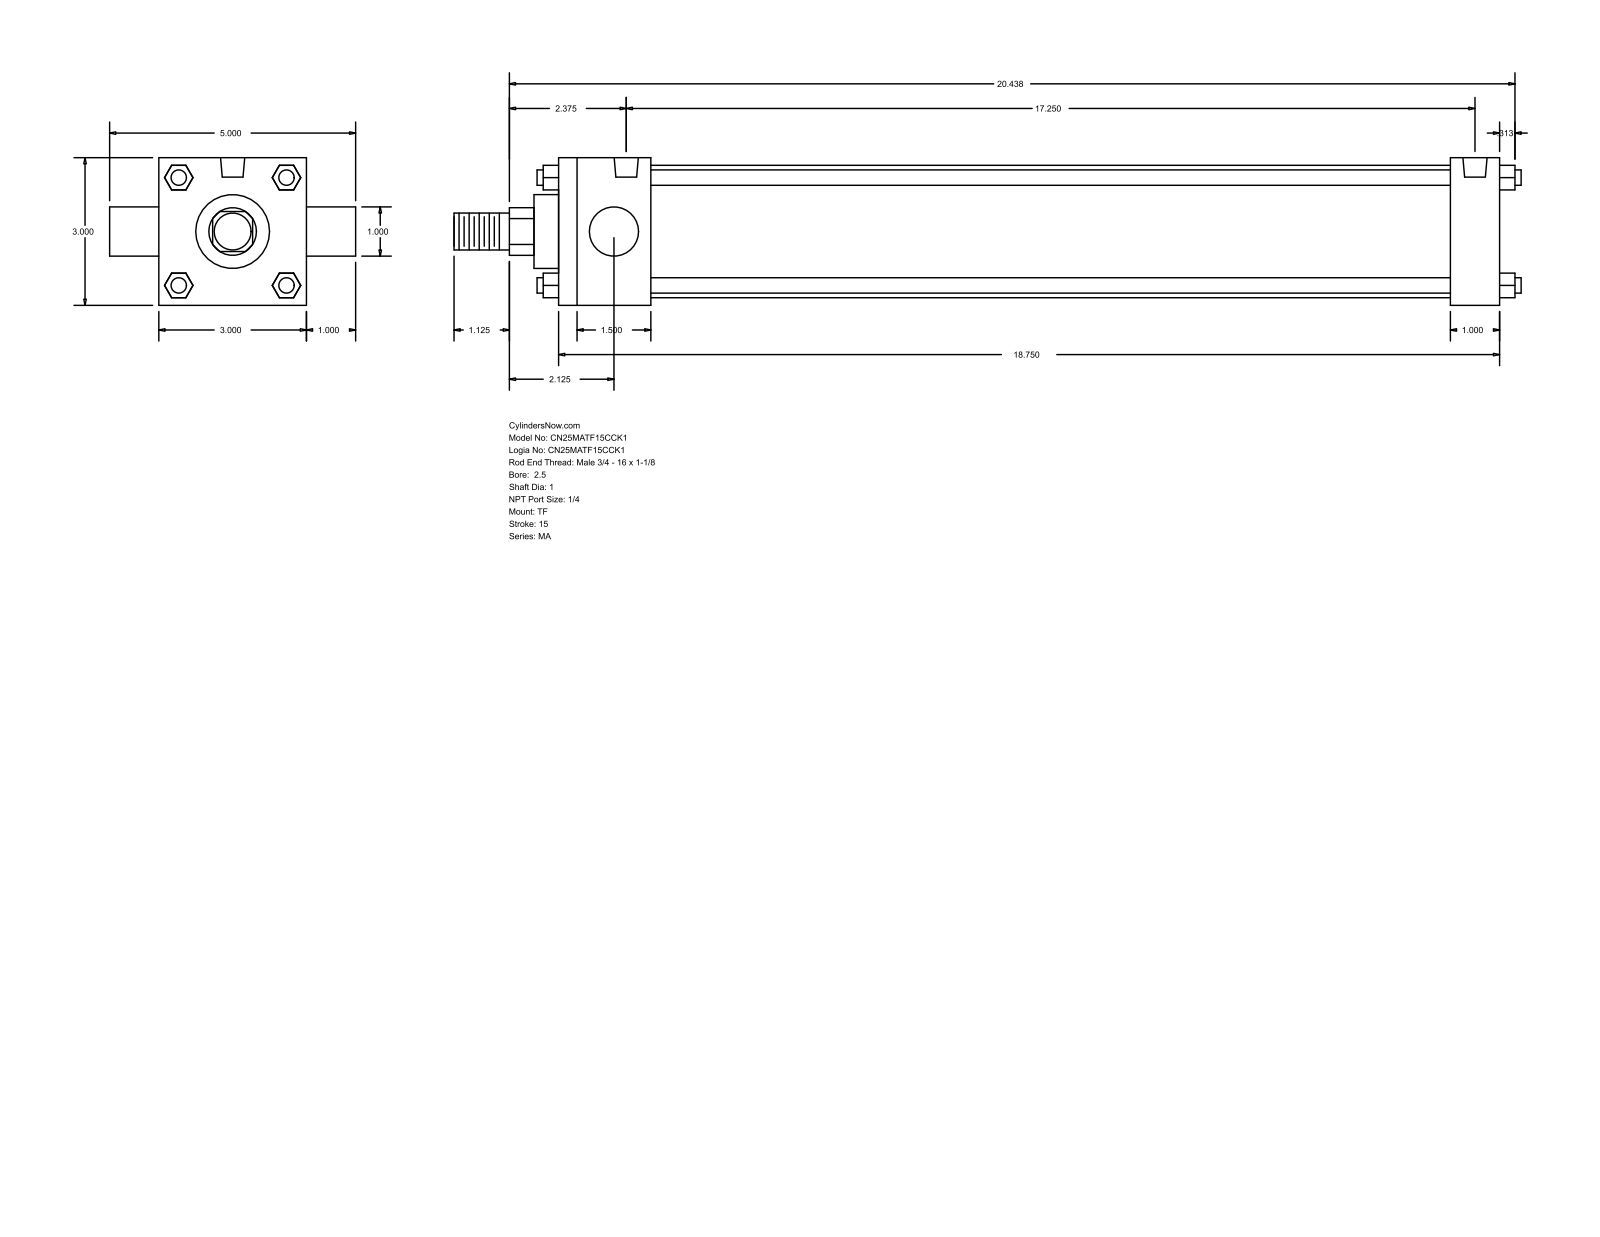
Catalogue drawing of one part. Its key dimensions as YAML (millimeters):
part_name: "MA_TF__0250_1"
step_written_by: "GSSL Pune (CONFIG_CONTROL_DESIGN)"
units: millimeters
bodies: {solids: 0, faces: 120, planar: 92, cylindrical: 28, other: 0}
overall_size: [550.86, 127, 76.2]
round_holes:
  - {diameter: 7.94, count: 3}
  - {diameter: 12.49, count: 2}
round_bosses_or_shafts:
  - {diameter: 7.94, count: 4}
  - {diameter: 25.4, count: 2}
  - {diameter: 68.33, count: 1}
  - {diameter: 38.1, count: 1}
  - {diameter: 19.05, count: 1}
partial_cylinders:
  - {radius: 12.29, count: 1}
face_to_face_distances: [76.2, 485.78, 12.7, 47.63, 460.37, 412.74, 438.15, 25.41, 101.6, 25.4]
hole_center_spacings: [438.15]
